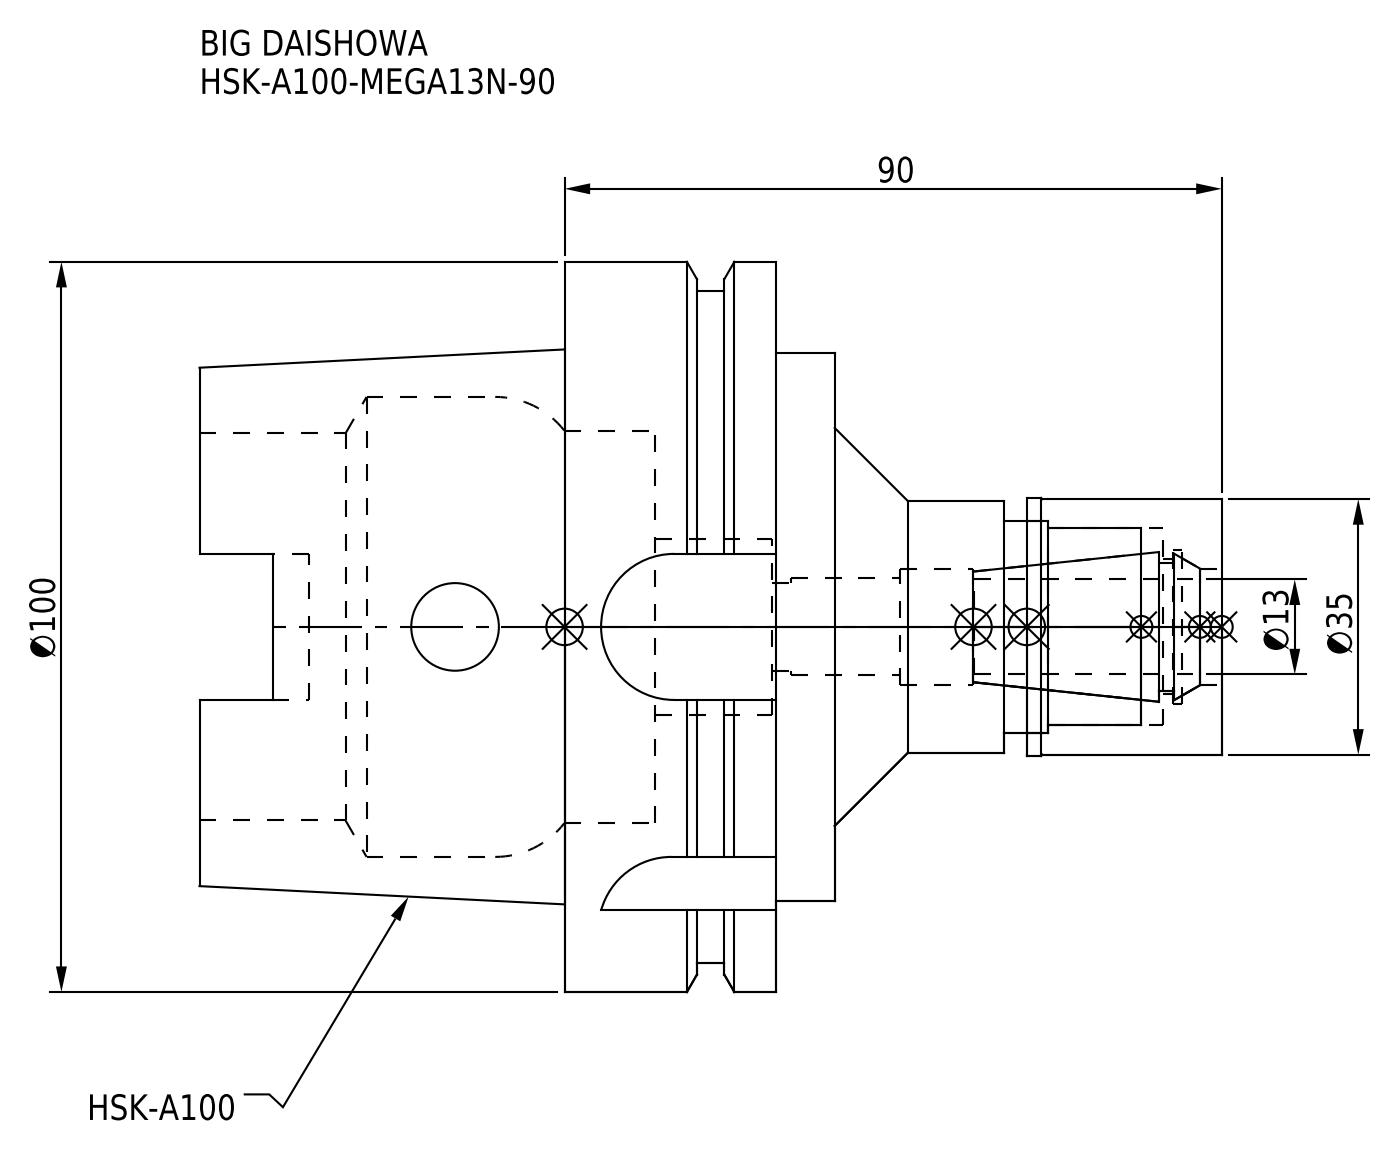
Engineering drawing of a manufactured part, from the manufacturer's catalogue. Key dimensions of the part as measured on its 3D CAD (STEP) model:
Part name (STEP PRODUCT): HSK-A100-MEGA13N-90; DXF_TEMP_ASSY_ASM_4_ASM.stp; MGN13_1.stp; HSK-A100-MEGA13N-90_1.stp (+3 more)
STEP written by: SolidWorks 2019 (CONFIG_CONTROL_DESIGN)
Units: millimetres
Bodies: 2 solids, 124 faces (44 planar, 58 cylindrical, 22 other)
Overall size (bounding box): 140 × 100 × 100
Volume: 331 215 mm³ · Surface area: 64 339 mm²
Round holes (diameter × count): ⌀12 ×2, ⌀13.3 ×1, ⌀16 ×1, ⌀18.5 ×1, ⌀21 ×1, ⌀24 ×1, ⌀27 ×1, ⌀29 ×1, ⌀53 ×1, ⌀53.8 ×1, ⌀63 ×1
Round bosses / shafts (diameter × count): ⌀100 ×1, ⌀92 ×1, ⌀75 ×1, ⌀35.3 ×1, ⌀35 ×1, ⌀34.5 ×1
Partial cylindrical surfaces — rounded edges, fillets, slot ends (radius × count): R4.88 ×4, R10 ×4
Main face-to-face distances: 29, 8, 37, 24.55, 16.55, 12.45, 50, 79, 53, 87
